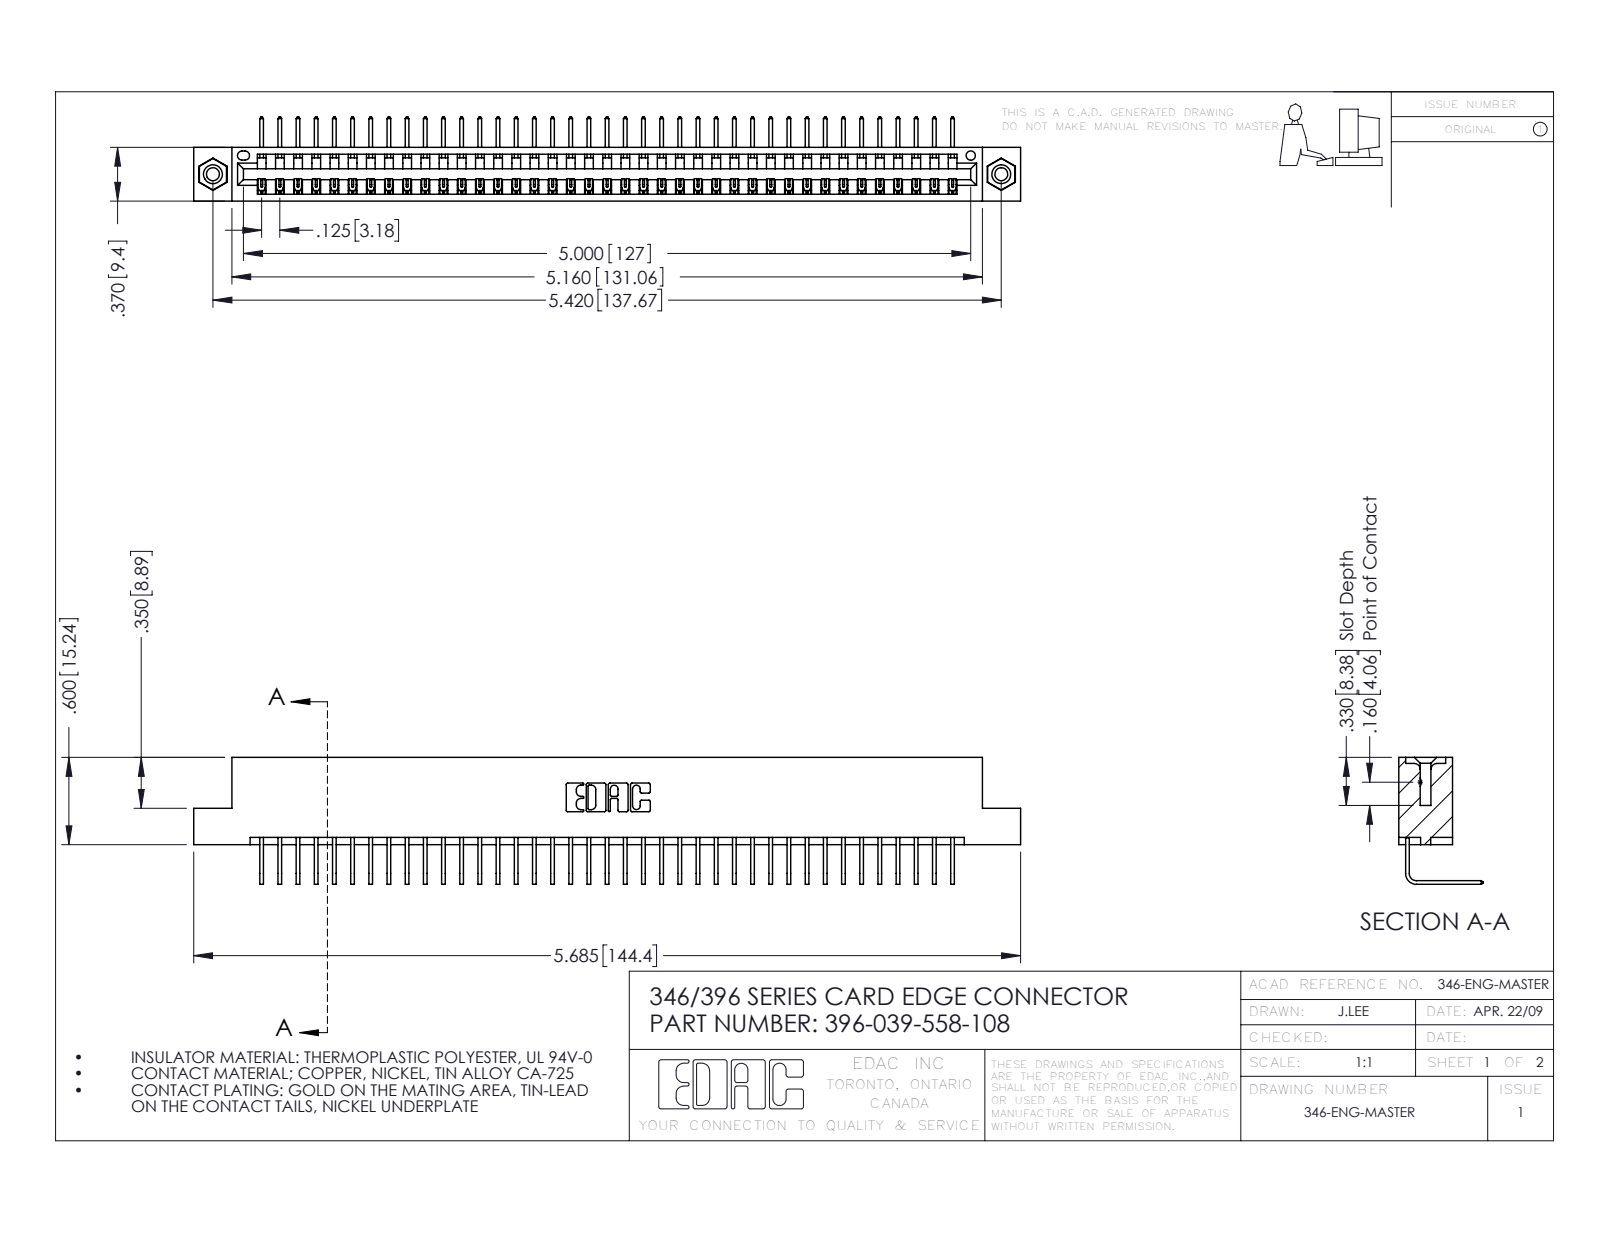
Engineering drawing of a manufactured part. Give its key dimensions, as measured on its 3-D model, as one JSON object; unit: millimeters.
{"part_name": "345-292-001_558 Tail - 2; 396-039-558-108; 345-250-001_345-250-003-102; 346 Part_Flush Mounting Lugs - 0.156 Dia-TI", "step_written_by": "SolidWorks 2016 (CONFIG_CONTROL_DESIGN)", "units": "millimeters", "bodies": {"solids": 42, "faces": 2522, "planar": 1746, "cylindrical": 760, "other": 16}, "overall_size": [144.4, 22.2, 14.7], "volume_mm3": 13900, "surface_area_mm2": 18170, "round_holes": [[2.3, 2], [3.2, 2], [4, 2], [1.6, 1]], "round_bosses_or_shafts": [[3.9, 2]], "partial_cylinders_radius": [[0.2, 78], [0.3, 22], [0.2, 6], [0.8, 6], [0.7, 3], [0.8, 2], [1, 2], [0.4, 1]], "face_to_face_distances": [8.2, 1.2, 9.4, 6.4, 7.6, 0.6, 1.8, 3.8, 5.6, 2.5], "hole_center_spacings": [6.2, 132.4, 137.7]}
